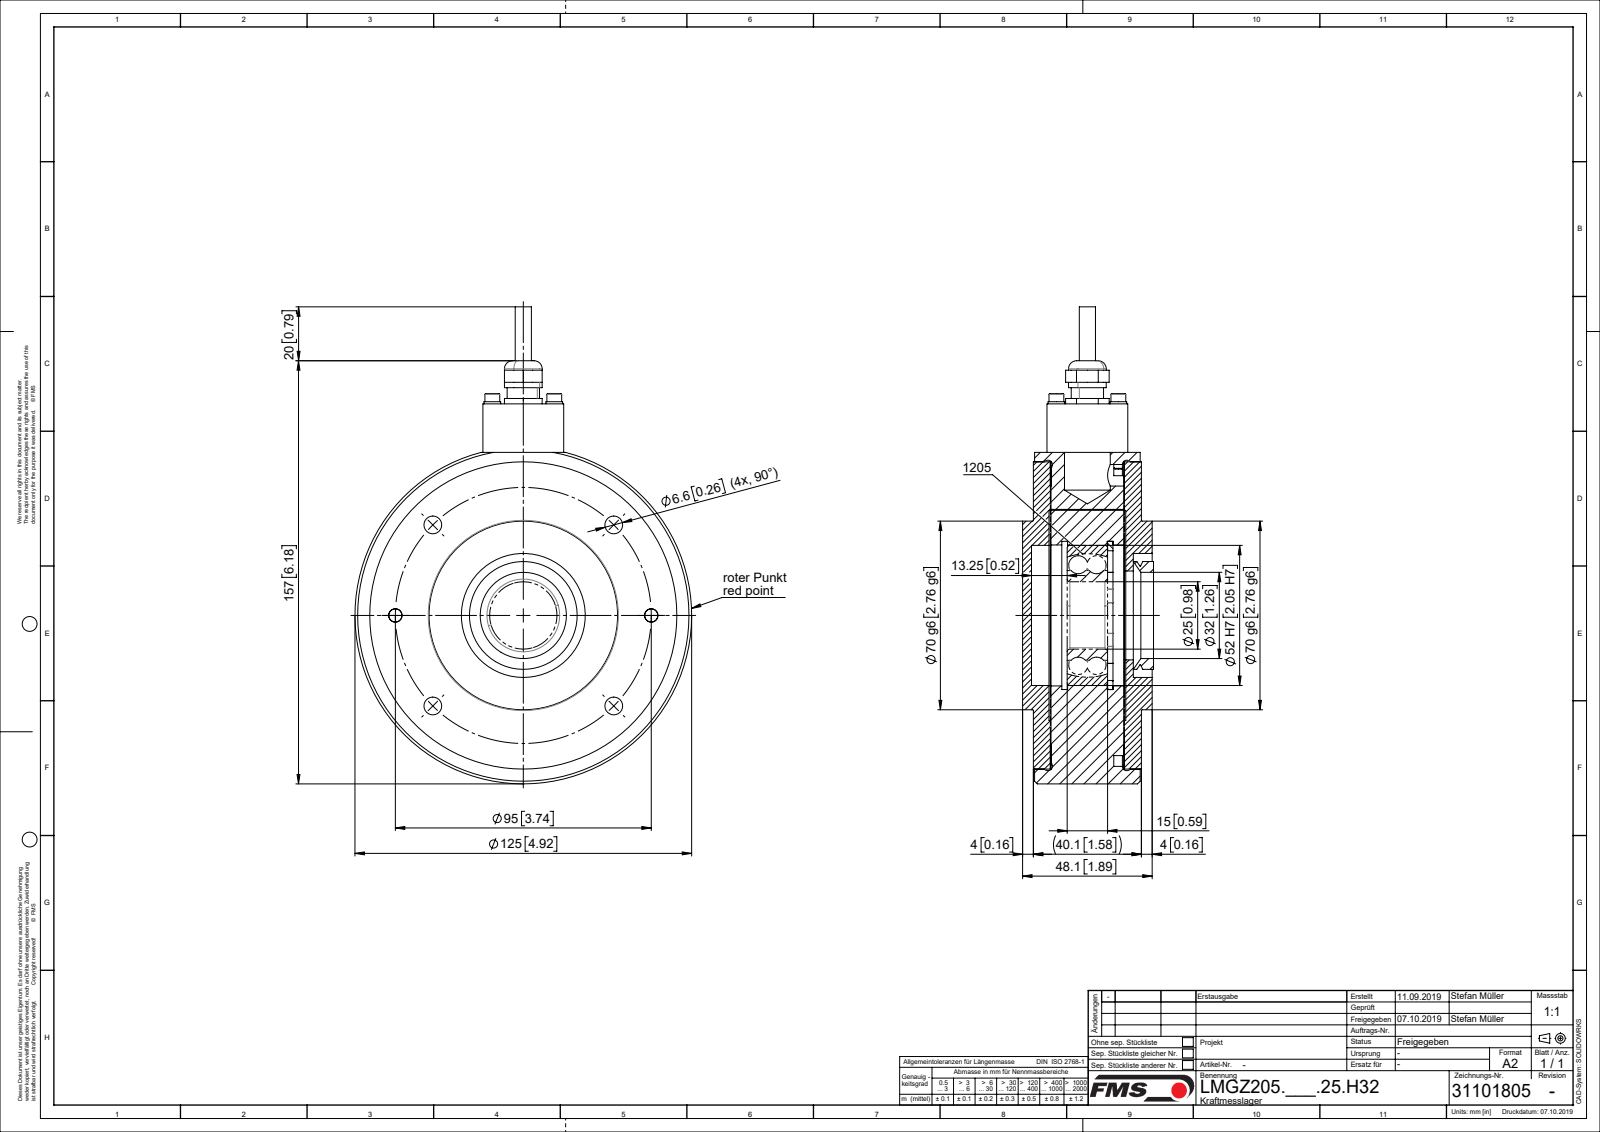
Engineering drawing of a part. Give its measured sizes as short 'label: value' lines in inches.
name: ZEICHNUNG7; ZEICHNUNG1; L49693; L4832404 (+8 more)
written by: Mechanical Desktop 2009 (CONFIG_CONTROL_DESIGN)
unit: in
bodies: 20 solids, 375 faces (111 planar, 212 cylindrical, 52 other)
size: 6.181 × 4.921 × 1.894
volume: 28.06 in³; area: 214.2 in²
holes: 6× ⌀0.26, 4× ⌀0.102, 4× ⌀0.126, 4× ⌀0.134, 2× ⌀0.197, 2× ⌀0.433, 1× ⌀0.236, 1× ⌀0.444, 1× ⌀0.906, 1× ⌀0.984, 1× ⌀1.22, 1× ⌀1.299
bosses: 4× ⌀0.244, 4× ⌀0.217, 4× ⌀0.118, 2× ⌀0.394, 2× ⌀0.236, 1× ⌀4.921, 1× ⌀4.488, 1× ⌀2.756
rounds: 8× R0.197, 1× R1.594, 1× R1.85
face distances: 1.073, 1.321, 0.248, 0.258, 1.331, 1.063, 1.083, 0.157, 0.415, 1.488
hole spacings: 1.87, 0.64, 0.906, 1.431, 2.645, 3.456, 1.281, 3.741
